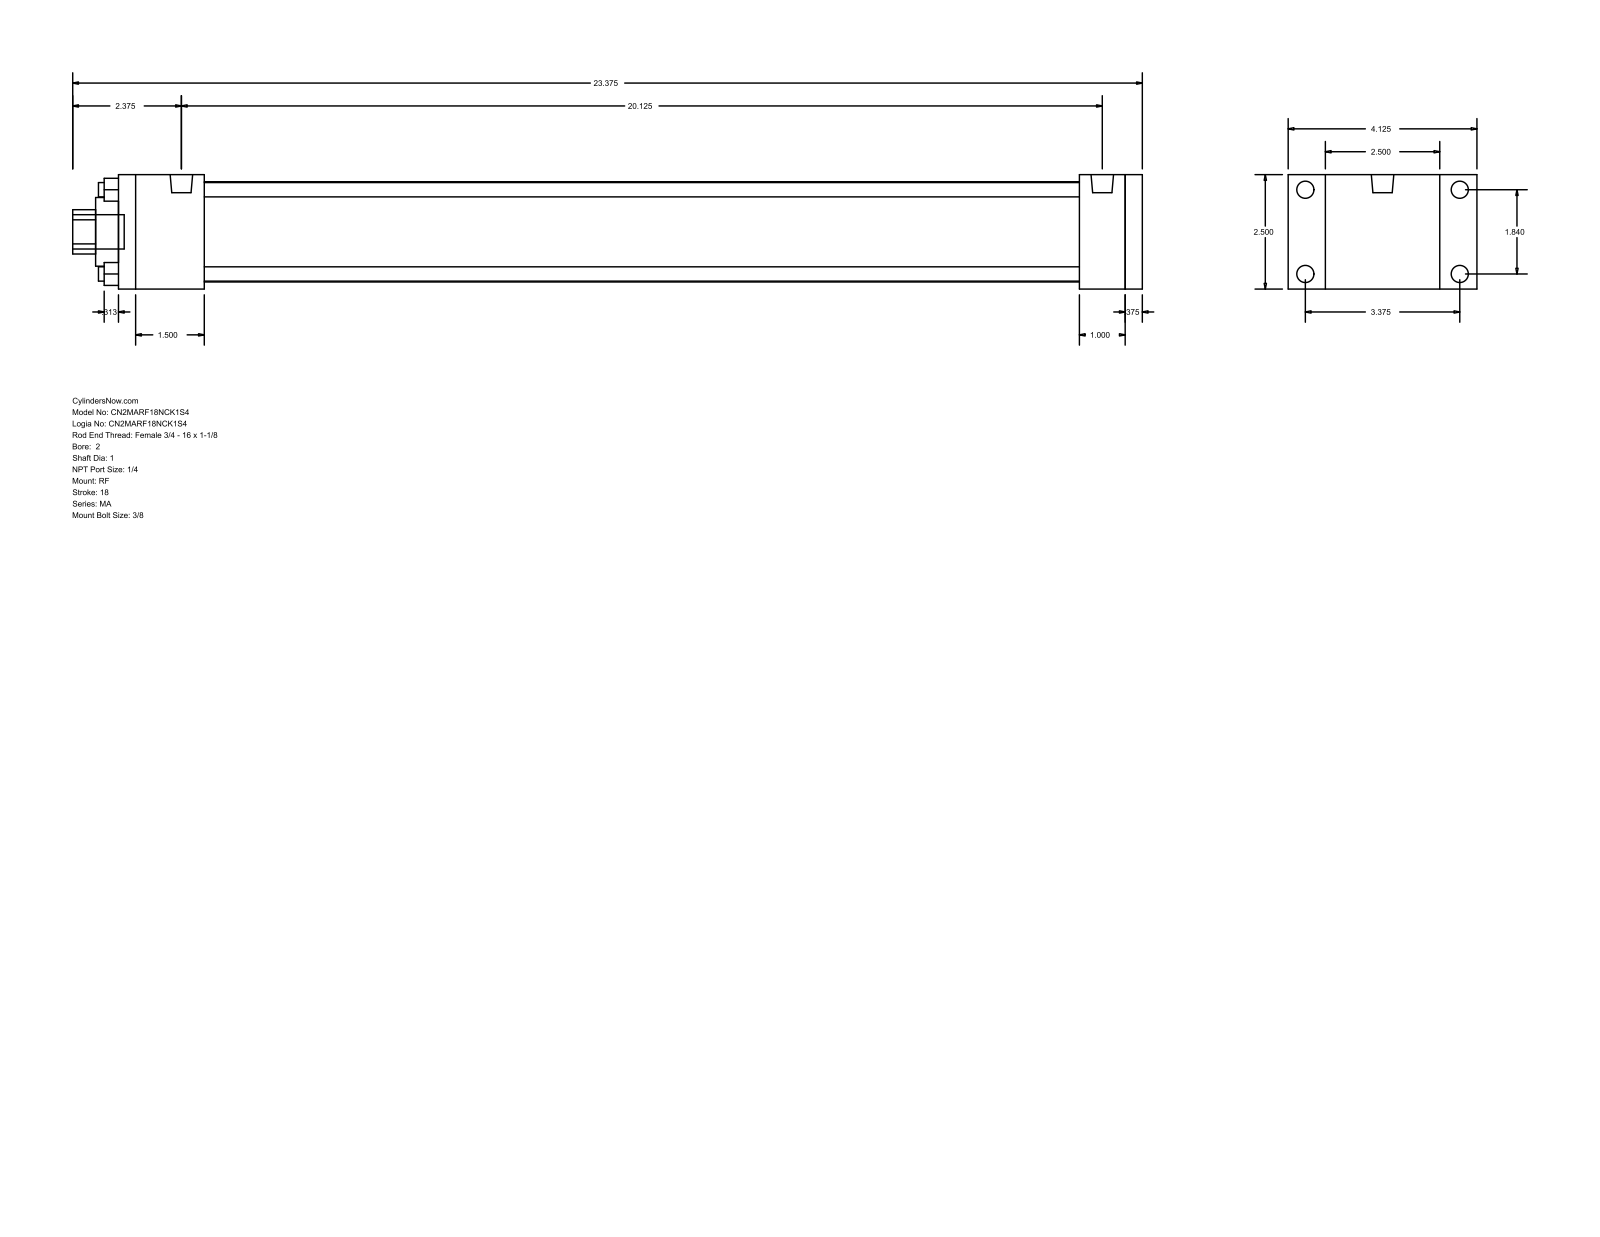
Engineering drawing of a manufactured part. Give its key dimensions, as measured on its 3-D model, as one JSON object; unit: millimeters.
{"part_name": "MA_RF__0200_1", "step_written_by": "GSSL Pune (CONFIG_CONTROL_DESIGN)", "units": "millimeters", "bodies": {"solids": 0, "faces": 92, "planar": 64, "cylindrical": 28, "other": 0}, "overall_size": [593.73, 104.78, 63.5], "round_holes": [[7.94, 4], [25.4, 1], [38.1, 1], [55.63, 1]], "round_bosses_or_shafts": [[9.53, 4], [7.94, 4], [12.49, 2], [19.05, 1]], "partial_cylinders_radius": [[12.29, 1]], "face_to_face_distances": [63.5, 558.8, 9.53, 568.33, 25.4, 20.64, 12.7, 47.63, 511.17, 520.7], "hole_center_spacings": [33.05, 46.74, 66.1]}
